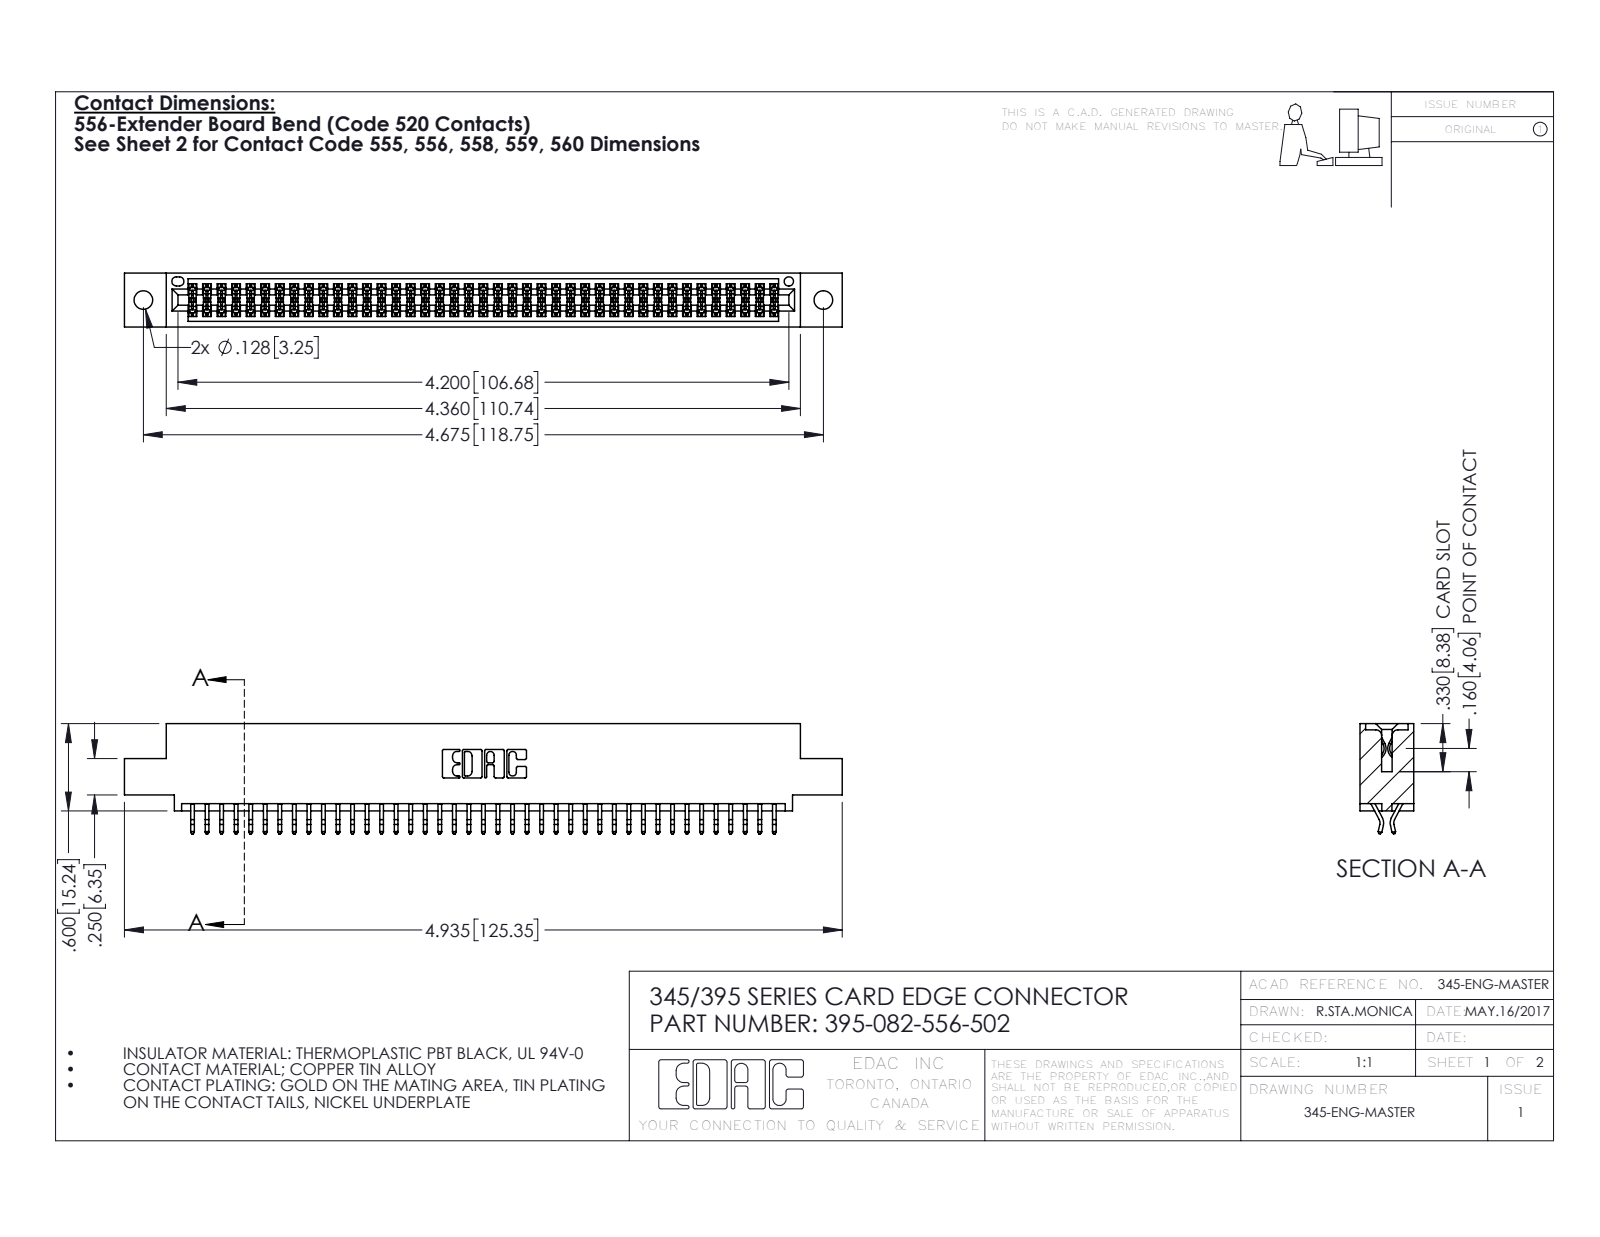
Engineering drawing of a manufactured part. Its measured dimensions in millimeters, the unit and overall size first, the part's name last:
Units: millimetres
Overall size (bounding box): 125.3 × 19.2 × 9.4
Round holes (diameter × count): ⌀3.3 ×2, ⌀1.6 ×1
Partial cylindrical surfaces — rounded edges, fillets, slot ends (radius × count): R0.2 ×123, R0.3 ×22, R0.2 ×6, R0.8 ×6, R0.7 ×3, R0.3 ×2, R0.4 ×2, R0.5 ×2
Main face-to-face distances: 7.6, 1.8, 9.4, 5.1, 0.6, 2.5, 6.9, 5.7, 4.4, 3.8
Hole centre spacings: 6.9, 112.8, 118.7
Volume: 12 100 mm³ · Surface area: 17 550 mm²
Bodies: 83 solids, 4722 faces (3118 planar, 1604 cylindrical, 0 other)
Part name (STEP PRODUCT): 395-082-556-502; 345-292-001_556 Tail; 345 Part_0.110 Offset - 0.128 Dia
STEP written by: SolidWorks 2016 (CONFIG_CONTROL_DESIGN)
